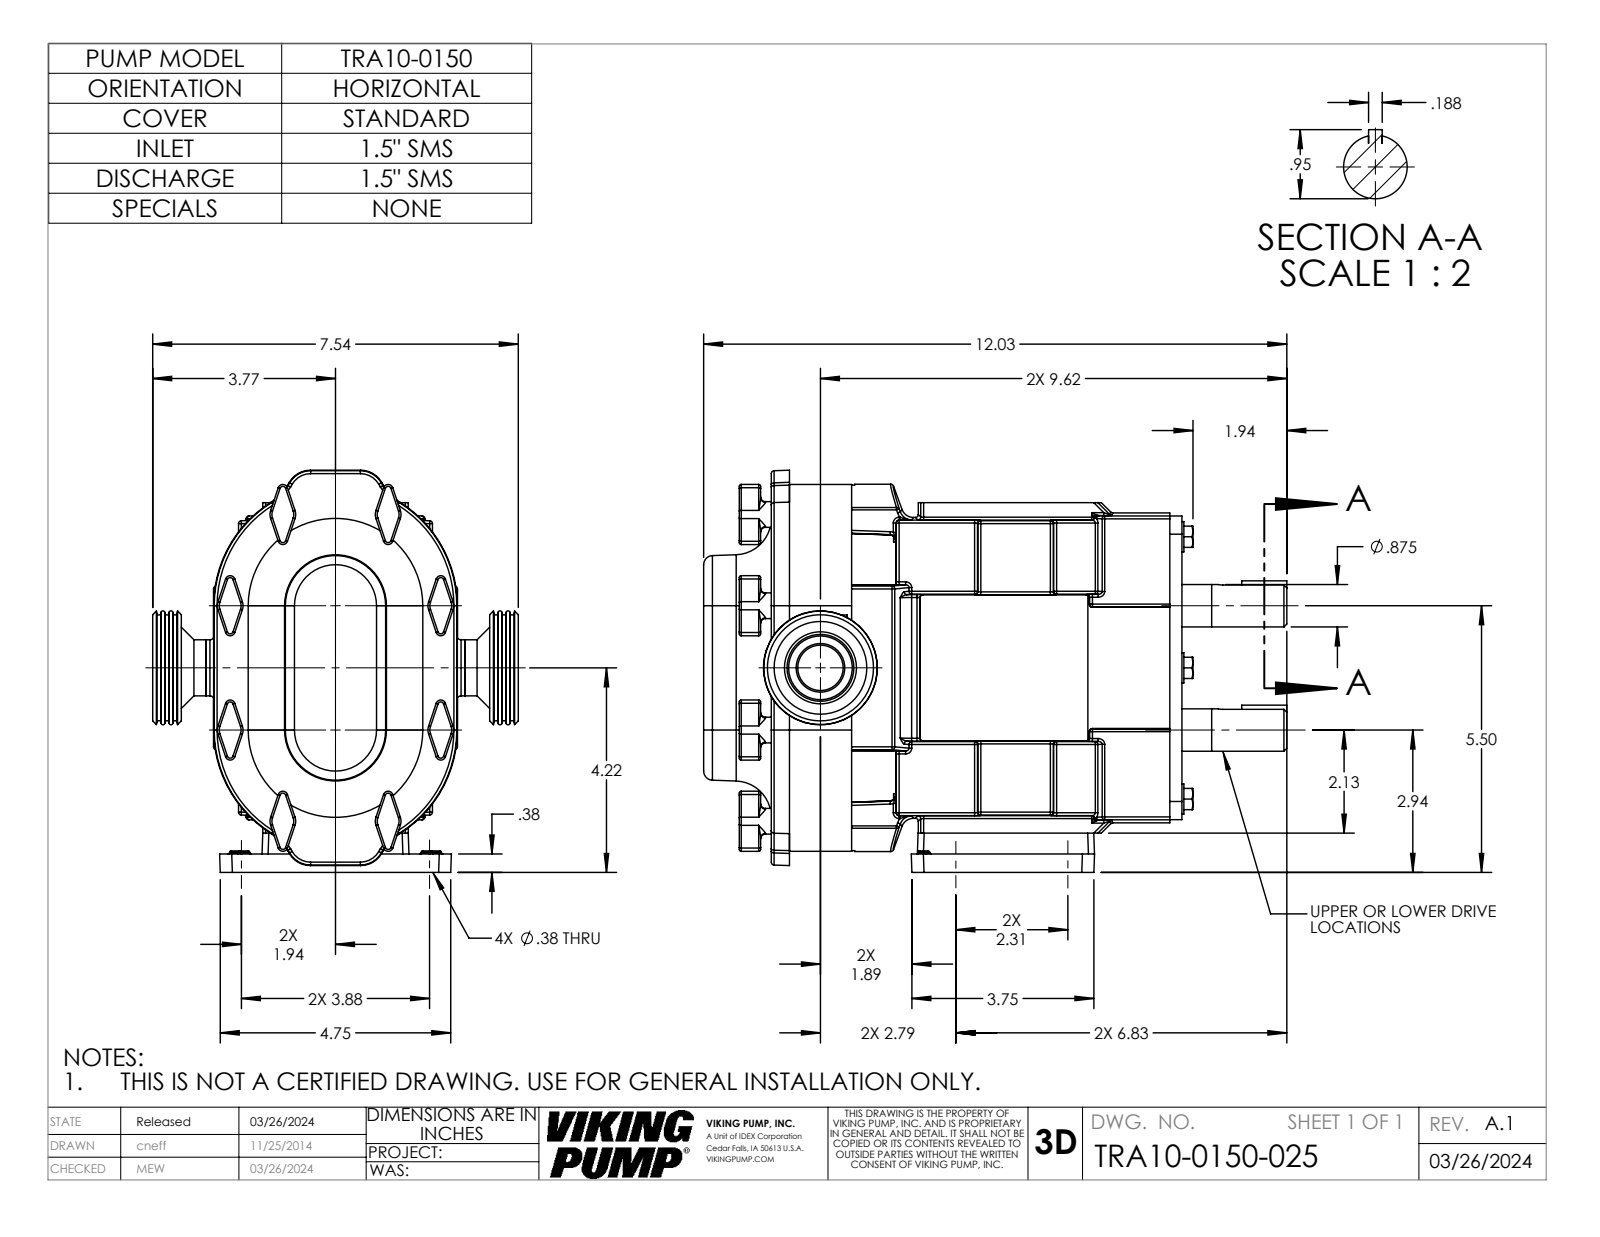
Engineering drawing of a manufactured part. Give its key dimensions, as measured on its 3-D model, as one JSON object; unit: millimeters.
{"part_name": "TRA10-0150-GEARBOX-H; 0150SMS15; TRA10-0150-BODY; TRA10-0150-COVER-STD (+1 more)", "step_written_by": "SolidWorks 2022 (AUTOMOTIVE_DESIGN)", "units": "millimeters", "bodies": {"solids": 5, "faces": 1261, "planar": 323, "cylindrical": 453, "other": 485}, "overall_size": [305.5, 210.6, 191.5], "volume_mm3": 3874000, "surface_area_mm2": 324400, "round_holes": [[9.5, 4], [23.8, 1], [35.1, 1], [48.6, 1]], "round_bosses_or_shafts": [[13.5, 8], [15.9, 6], [22.2, 2], [37.7, 1], [29.4, 1]], "partial_cylinders_radius": [[1.5, 189], [1, 64], [3.2, 20], [0.8, 16], [2.5, 16], [6.4, 14], [9.5, 4], [12.7, 4]], "face_to_face_distances": [32.6, 205.6, 173.1, 9.5, 61.1, 28.6, 144.4, 12.6, 95.4, 3.2], "hole_center_spacings": [58.7, 98.6, 114.7]}
